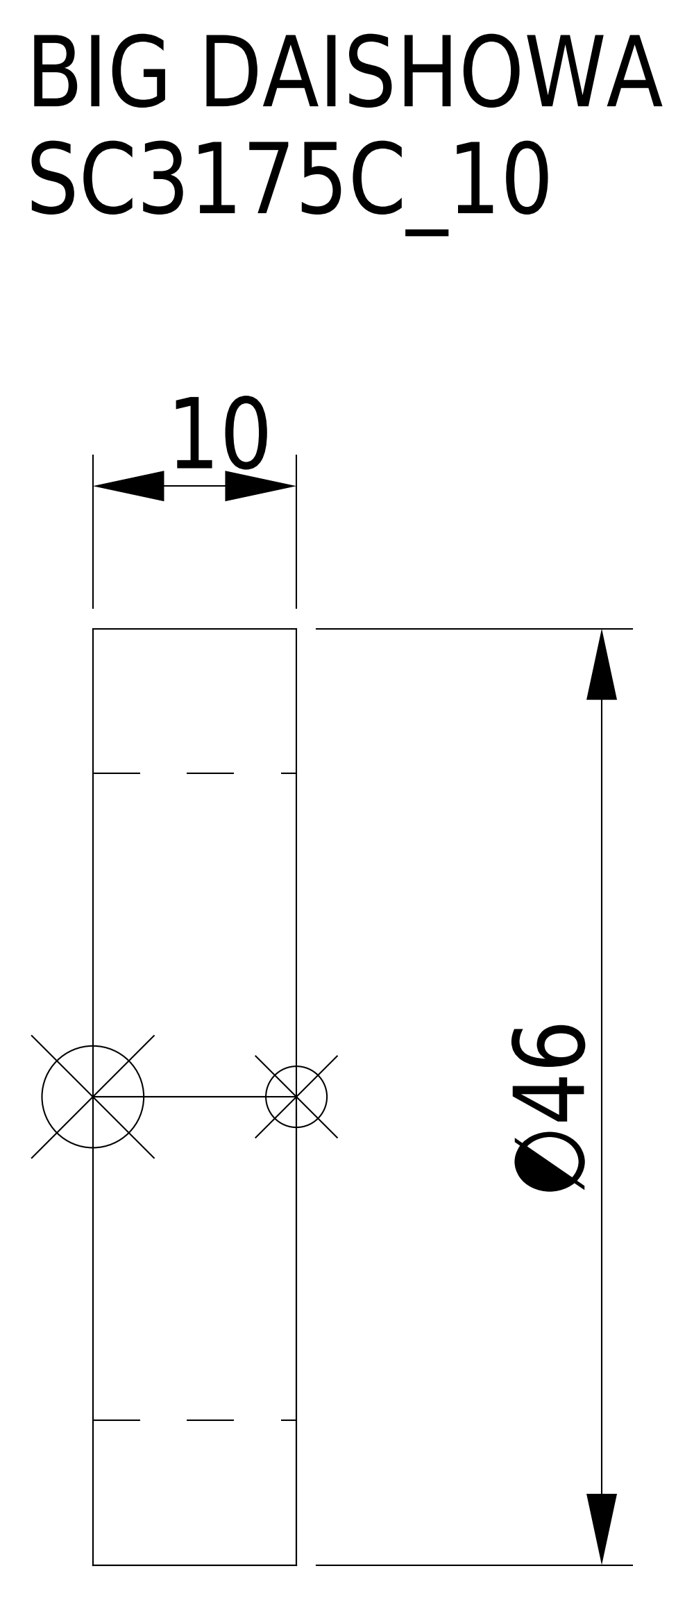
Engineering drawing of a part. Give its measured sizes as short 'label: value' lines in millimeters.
name: SC3175C_10
written by: CREO PARAMETRIC BY PTC INC, 2016380 (AUTOMOTIVE_DESIGN)
unit: mm
bodies: 1 solid, 8 faces (5 planar, 3 cylindrical, 0 other)
size: 46 × 46 × 10
volume: 8 408 mm³; area: 4 203 mm²
holes: 1× ⌀31.75
bosses: 1× ⌀46
face distances: 10, 8.1
